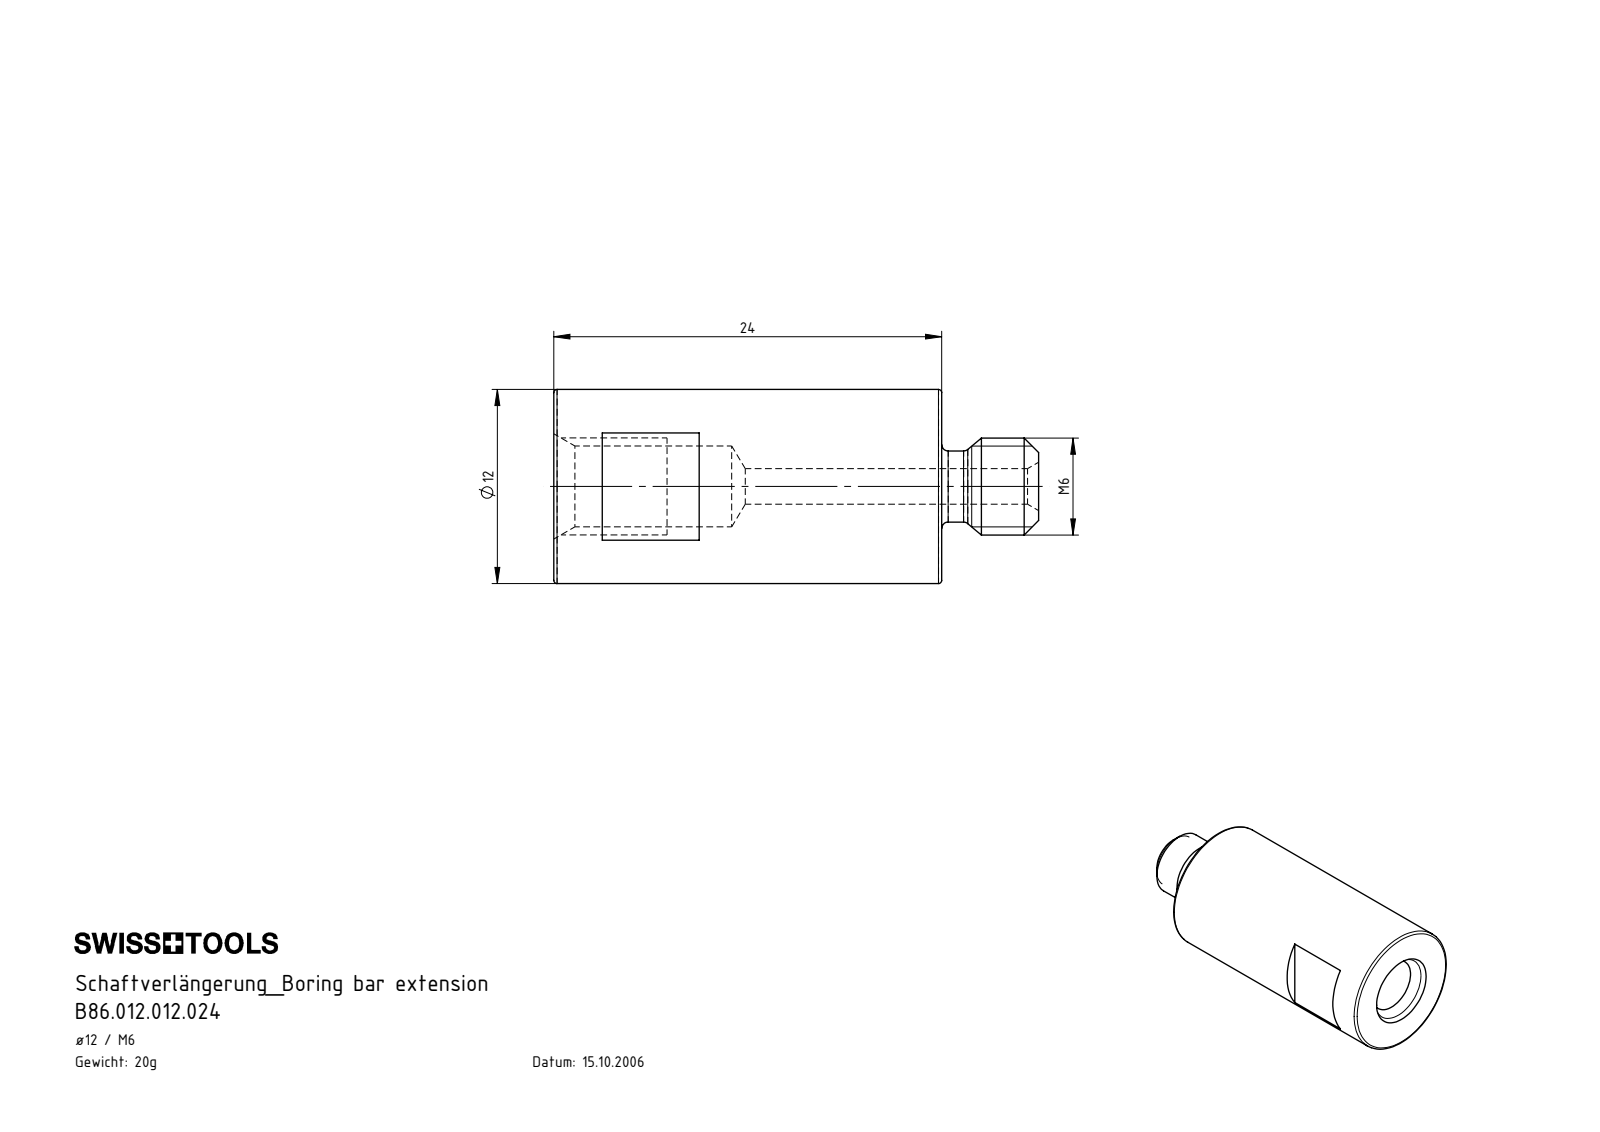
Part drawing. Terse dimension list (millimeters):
name: B86.012.012.024
written by: SolidWorks 2022 (CONFIG_CONTROL_DESIGN)
unit: mm
bodies: 1 solid, 37 faces (9 planar, 10 cylindrical, 18 other)
size: 30 × 12 × 12
volume: 2 493 mm³; area: 1 530 mm²
holes: 1× ⌀2.2, 1× ⌀5
bosses: 1× ⌀12, 1× ⌀6, 1× ⌀4.4
face distances: 24, 10, 21, 6, 3, 15, 9, 27, 30
